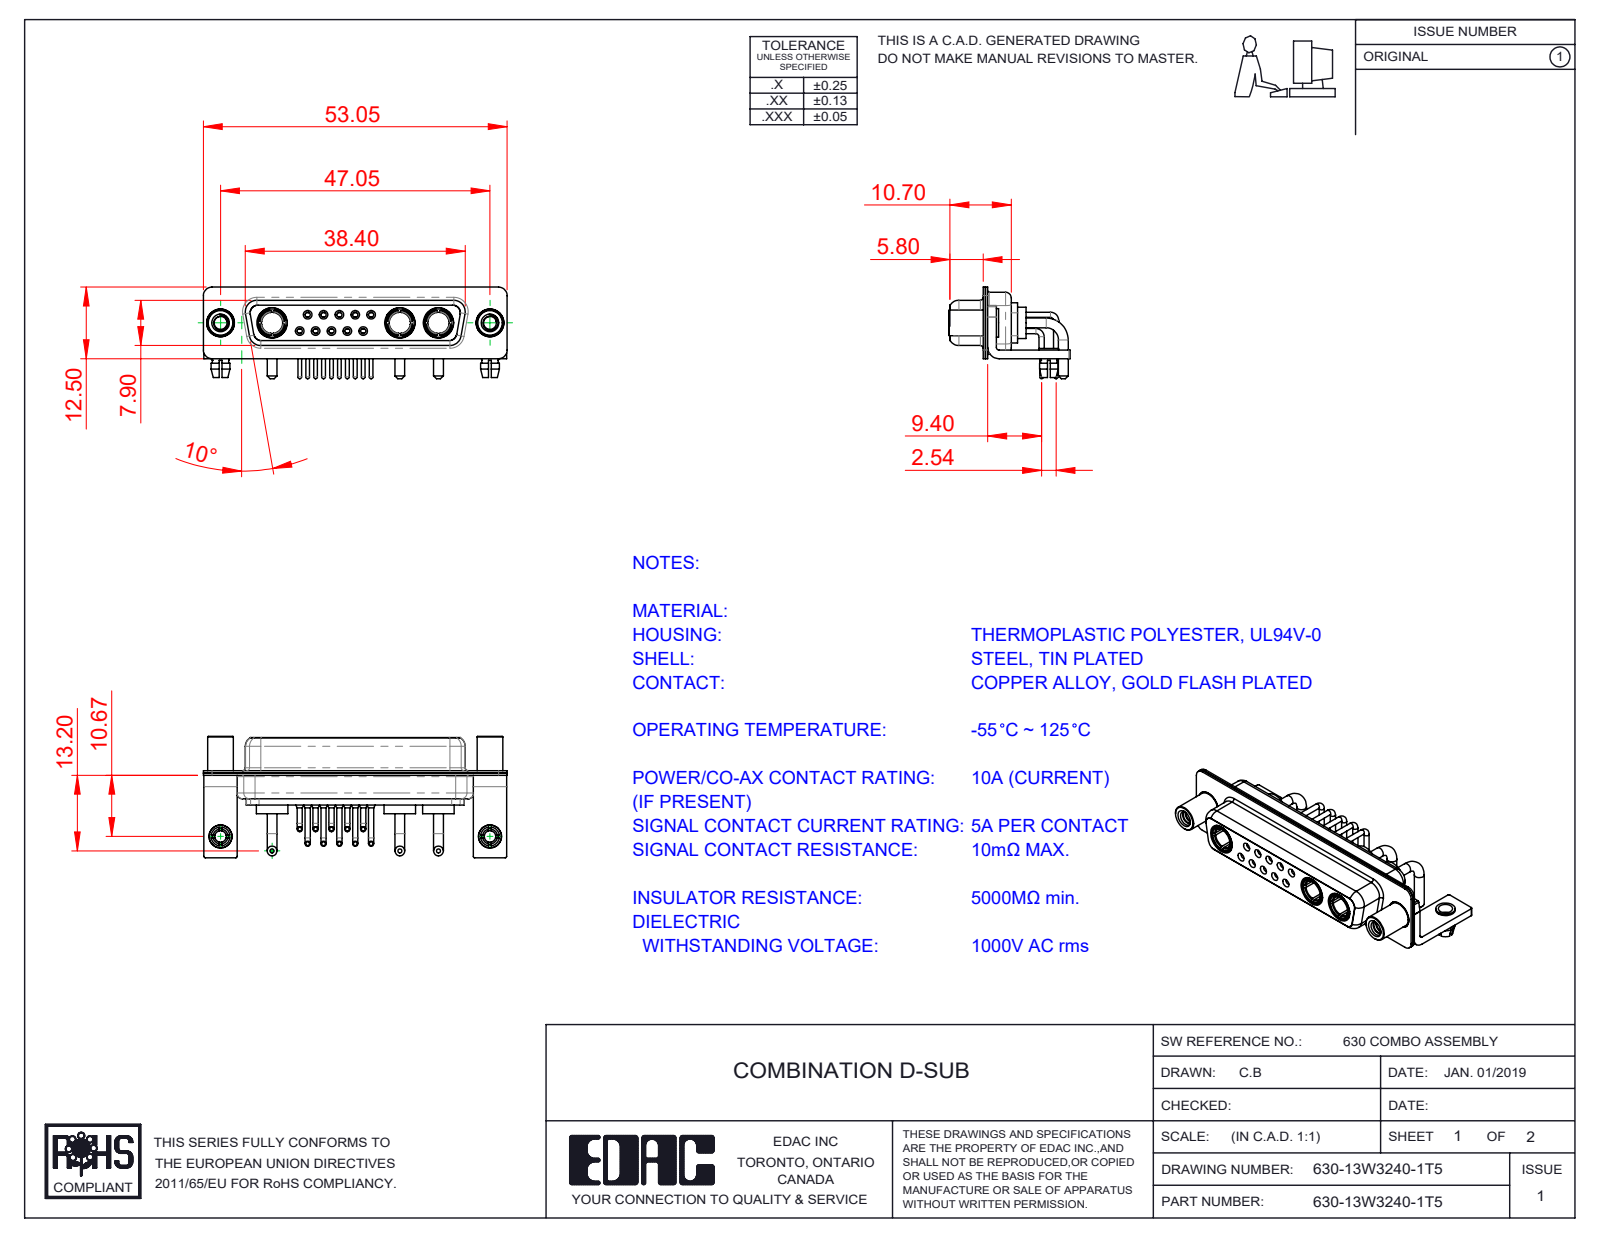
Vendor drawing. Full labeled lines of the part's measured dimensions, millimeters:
Part name (STEP PRODUCT): 630Combo Housing_13W3; 630Combo Stabilizer Bracket; 630Combo Contact Row 1; 630-13W3240-1T5 (+6 more)
STEP written by: SolidWorks 2020 (CONFIG_CONTROL_DESIGN)
Units: millimetres
Bodies: 25 solids, 1223 faces (374 planar, 534 cylindrical, 315 other)
Overall size (bounding box): 53.05 × 21.2 × 16
Volume: 4 285 mm³ · Surface area: 9 992 mm²
Round holes (diameter × count): ⌀2 ×12, ⌀0.9 ×10, ⌀1.1 ×10, ⌀1.5 ×10, ⌀1.6 ×5, ⌀1.7 ×5, ⌀4.85 ×5, ⌀3.7 ×3, ⌀5.3 ×3, ⌀2.26 ×2, ⌀2.5 ×2, ⌀3.2 ×2
Round bosses / shafts (diameter × count): ⌀0.9 ×10, ⌀0.65 ×10, ⌀1.7 ×6, ⌀1.6 ×5, ⌀5.5 ×3, ⌀5.2 ×3, ⌀4.96 ×3, ⌀4.75 ×3
Partial cylindrical surfaces — rounded edges, fillets, slot ends (radius × count): R0.25 ×16, R1.5 ×16, R2 ×13, R1.35 ×8, R1.6 ×8, R0.5 ×5, R0.6 ×4, R0.65 ×4
Main face-to-face distances: 0.4, 0.45, 1.4, 8.45, 1.8, 8.9, 0.8, 1.5, 6.2, 7.05
Hole centre spacings: 3.16, 2.77, 5.54, 5.03, 5.04, 8.31, 7.48, 7.49
